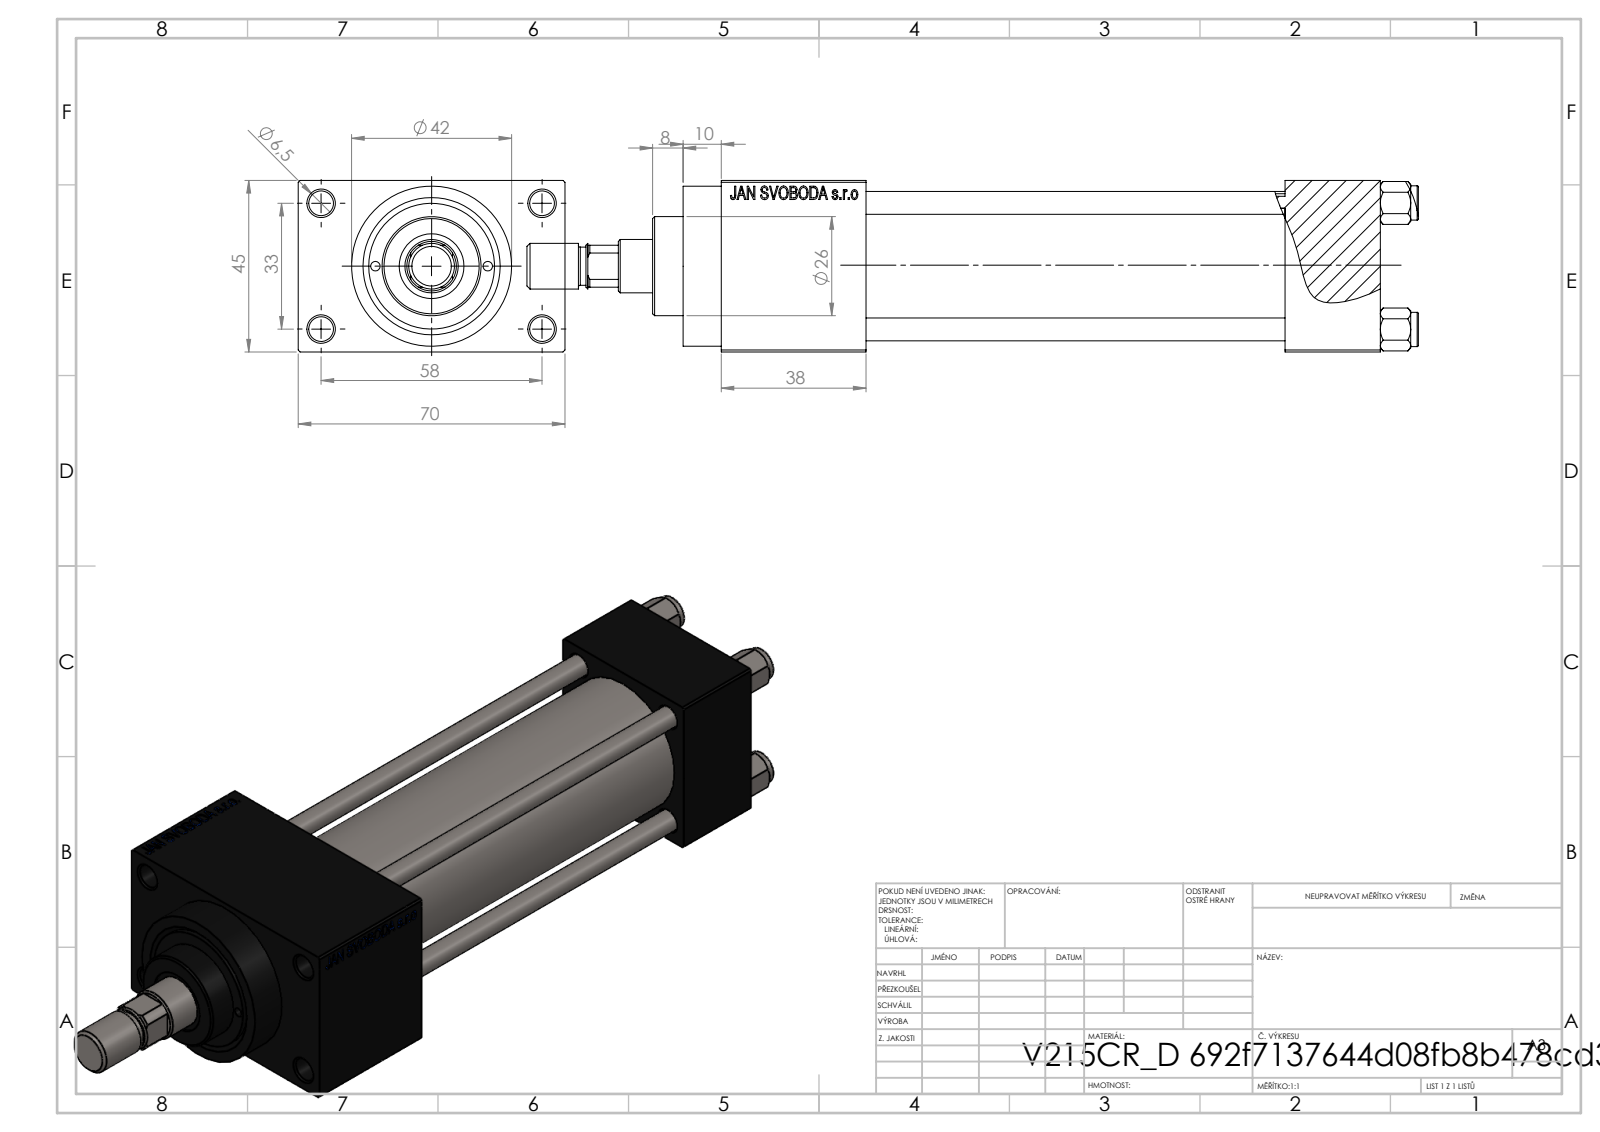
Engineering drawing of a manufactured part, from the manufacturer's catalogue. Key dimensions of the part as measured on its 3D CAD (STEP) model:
Part name (STEP PRODUCT): V215_VC_A; NUT_M5_D; V215CR_D_Body; V215CR_D_TYCINKA (+2 more)
STEP written by: SolidWorks 2019 (CONFIG_CONTROL_DESIGN)
Units: millimetres
Bodies: 12 solids, 1124 faces (502 planar, 96 cylindrical, 526 other)
Overall size (bounding box): 234 × 70 × 45
Volume: 267 698 mm³ · Surface area: 96 586 mm²
Round holes (diameter × count): ⌀6.5 ×5, ⌀6 ×4, ⌀2.5 ×2, ⌀7 ×2, ⌀13.16 ×2, ⌀20 ×2, ⌀14 ×1, ⌀17 ×1, ⌀24 ×1, ⌀32 ×1, ⌀33 ×1
Round bosses / shafts (diameter × count): ⌀9 ×4, ⌀42 ×1, ⌀38 ×1, ⌀26 ×1, ⌀12 ×1, ⌀10 ×1
Partial cylindrical surfaces — rounded edges, fillets, slot ends (radius × count): R6.5 ×1
Main face-to-face distances: 45, 25, 12.5, 110, 135, 57.5, 148, 38, 173, 70
Hole centre spacings: 12.4, 16.7, 21.8, 23.48, 33.2, 33.37, 35.35, 35.47
